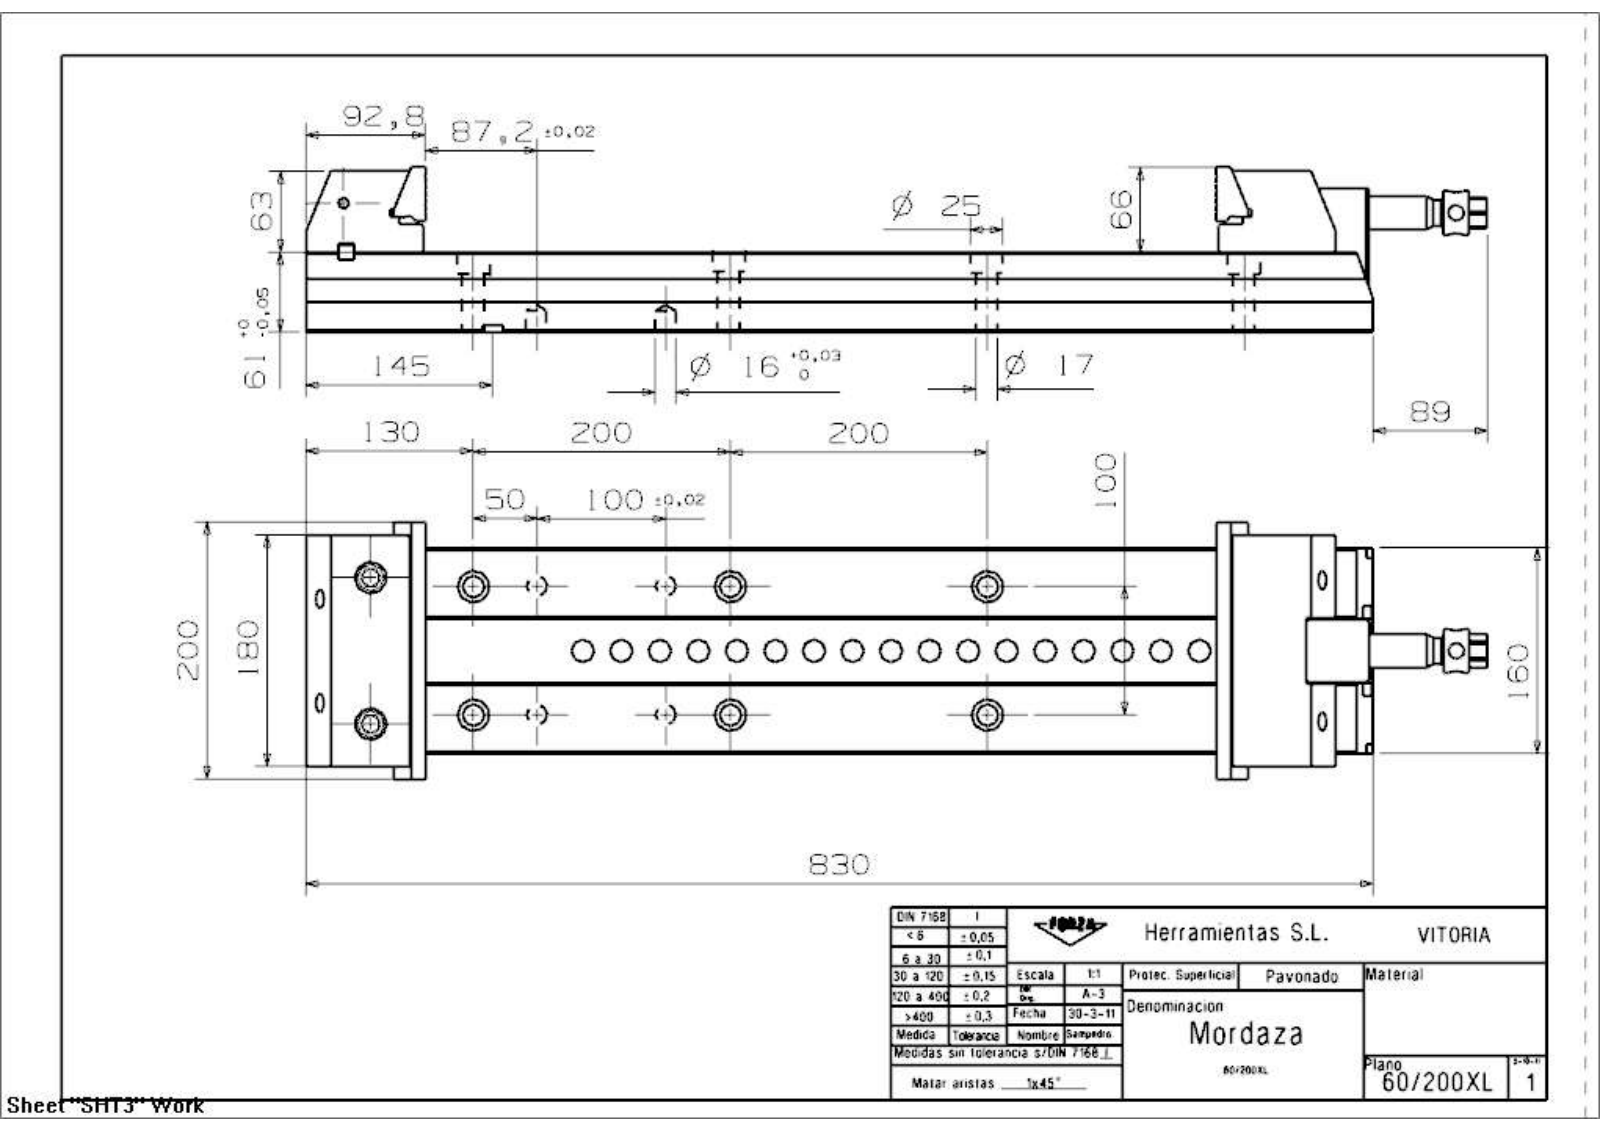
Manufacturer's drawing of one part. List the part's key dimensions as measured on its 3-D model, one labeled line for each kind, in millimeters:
Part name (STEP PRODUCT): 60_200XL_Mordaza
STEP written by: SIEMENS PLM Software NX 7.5 (CONFIG_CONTROL_DESIGN)
Units: millimetres
Bodies: 15 solids, 594 faces (332 planar, 145 cylindrical, 117 other)
Overall size (bounding box): 919 × 200 × 127.95
Volume: 8 116 000 mm³ · Surface area: 828 196 mm²
Round holes (diameter × count): ⌀17 ×10, ⌀25 ×10, ⌀15 ×6, ⌀16 ×5, ⌀6.99 ×4, ⌀8.5 ×4, ⌀10 ×4, ⌀8.78 ×3, ⌀10.58 ×3, ⌀5 ×2, ⌀12 ×2, ⌀12.38 ×2
Round bosses / shafts (diameter × count): ⌀24 ×2, ⌀21 ×2, ⌀15.68 ×2, ⌀13.68 ×2, ⌀34 ×1, ⌀33.8 ×1, ⌀26 ×1, ⌀20 ×1
Partial cylindrical surfaces — rounded edges, fillets, slot ends (radius × count): R0.4 ×24, R20 ×4, R1.6 ×2, R6 ×2, R7 ×2, R8 ×2, R4 ×1, R9 ×1
Main face-to-face distances: 62, 125, 29.3, 32.7, 60.5, 27.8, 160, 1.5, 45, 115
Hole centre spacings: 14.5, 95.5, 100, 114, 117.88, 200, 223.61, 30
